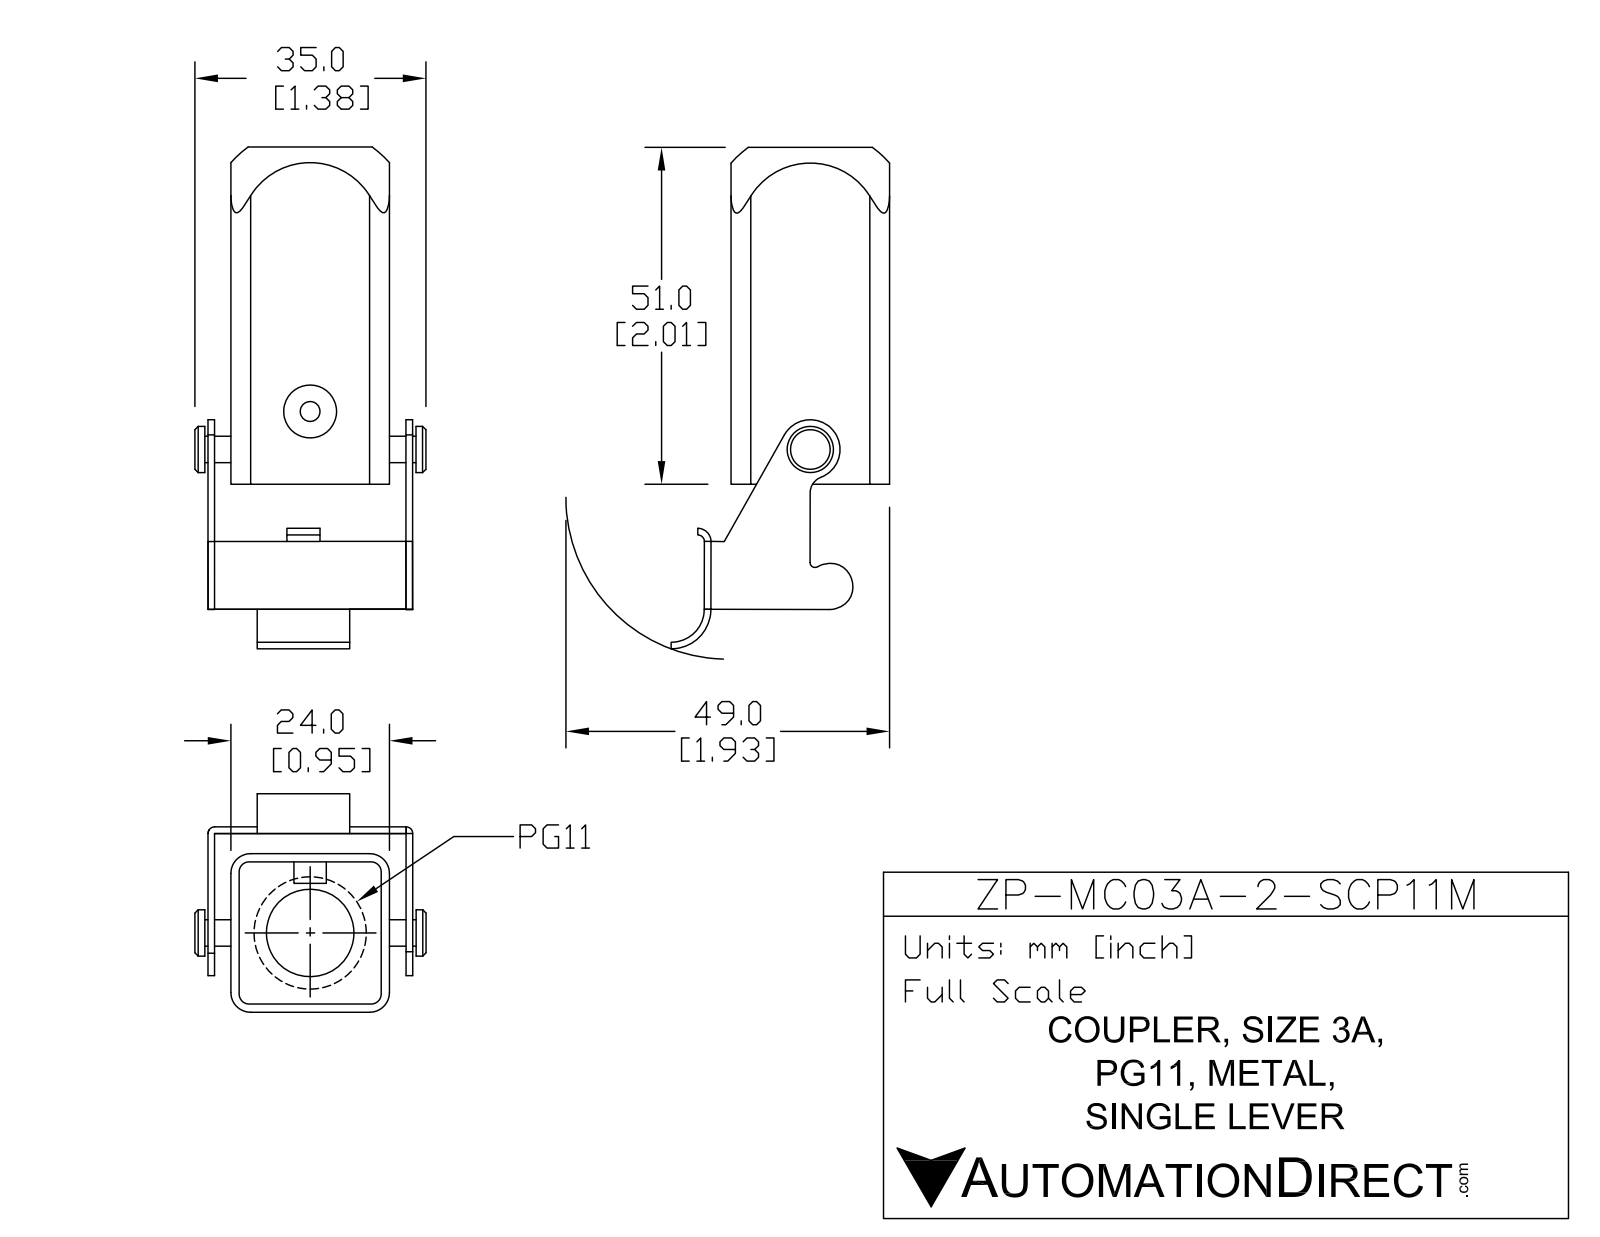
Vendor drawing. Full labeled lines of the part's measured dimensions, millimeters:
Part name (STEP PRODUCT): ZP-MC03A-2-SCP11M
STEP written by: SolidWorks 2011 (AUTOMOTIVE_DESIGN)
Units: millimetres
Bodies: 4 solids, 99 faces (48 planar, 43 cylindrical, 8 other)
Overall size (bounding box): 50.49 × 41.93 × 32
Volume: 9 114 mm³ · Surface area: 11 565 mm²
Round holes (diameter × count): ⌀3 ×1, ⌀4.5 ×1, ⌀13.25 ×1, ⌀17 ×1
Round bosses / shafts (diameter × count): ⌀7 ×1, ⌀4 ×1
Partial cylindrical surfaces — rounded edges, fillets, slot ends (radius × count): R1 ×7, R0.5 ×5, R1.5 ×4, R3 ×4, R5 ×2, R0.25 ×1, R1.4 ×1, R1.74 ×1
Main face-to-face distances: 1.25, 22.75, 24, 1, 21.5, 26, 2, 3.25, 24.75, 27
